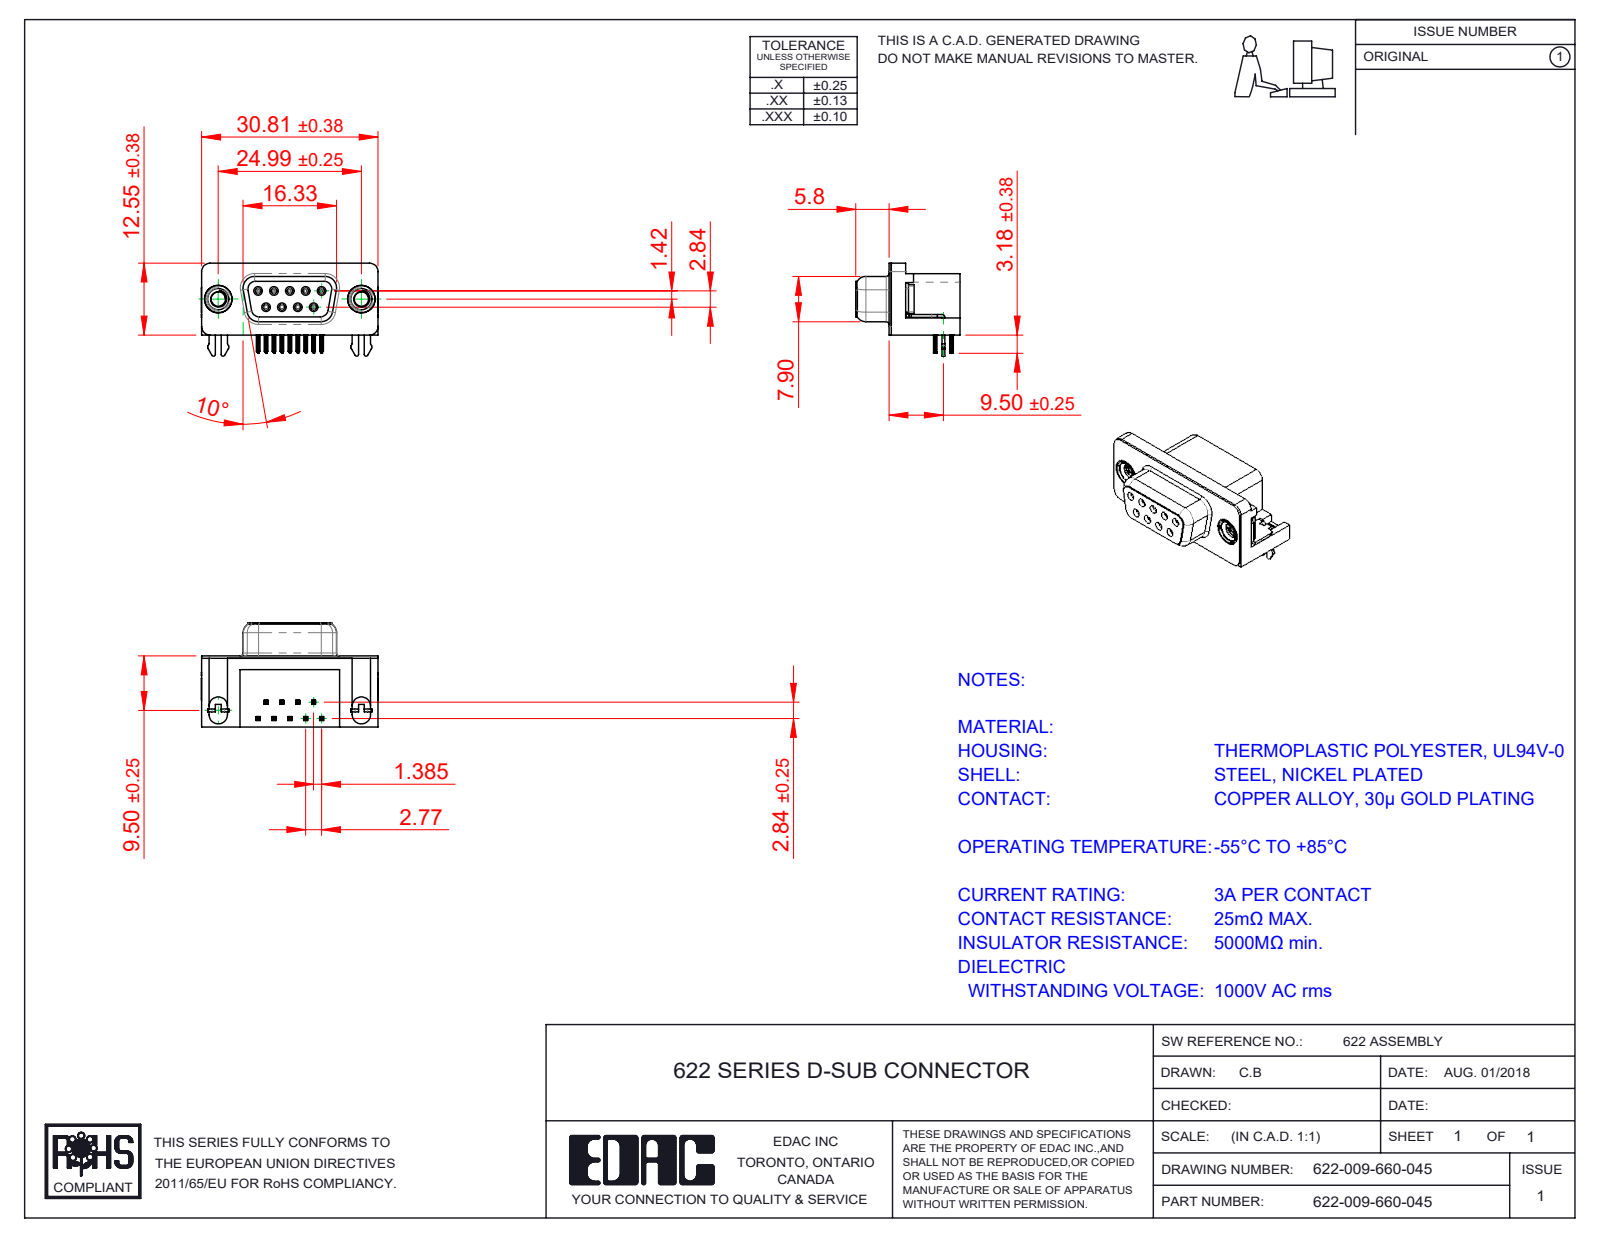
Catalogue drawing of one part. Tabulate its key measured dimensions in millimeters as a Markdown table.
| quantity | value |
| --- | --- |
| part name | 622 M3 Threaded Rivet; 622 Contact Top; 622 4 Prong Board Lock; 622-009-660-045 (+3 more) |
| STEP written by | SolidWorks 2016 (CONFIG_CONTROL_DESIGN) |
| units | millimeters |
| bodies | 15 solids, 1692 faces (726 planar, 426 cylindrical, 540 other) |
| overall size | 30.89 × 18.2 × 16.25 |
| volume | 3 730 mm³ |
| surface area | 5 151 mm² |
| round holes (diameter × count) | 0.8 × 9, 0.9 × 9, 2 × 2, 2.5 × 2, 4 × 2, 4.8 × 2, 5 × 2 |
| round bosses / shafts (diameter × count) | 1.2 × 9, 4.9 × 2, 4.75 × 2, 3.9 × 2, 3 × 2 |
| partial cylindrical surfaces (radius × count) | 0.1 × 72, 0.15 × 36, 0.35 × 18, 1 × 18, 0.25 × 12, 0.34 × 9, 1.35 × 8, 1.6 × 8 |
| main face-to-face distances | 0.4, 12, 12.4, 0.35, 2.9, 2.5, 6.2, 10.34, 9.5, 5.8 |
| hole center spacings | 3.16, 2.77, 5.54, 5.03, 5.04, 8.31, 7.48, 7.49 |
